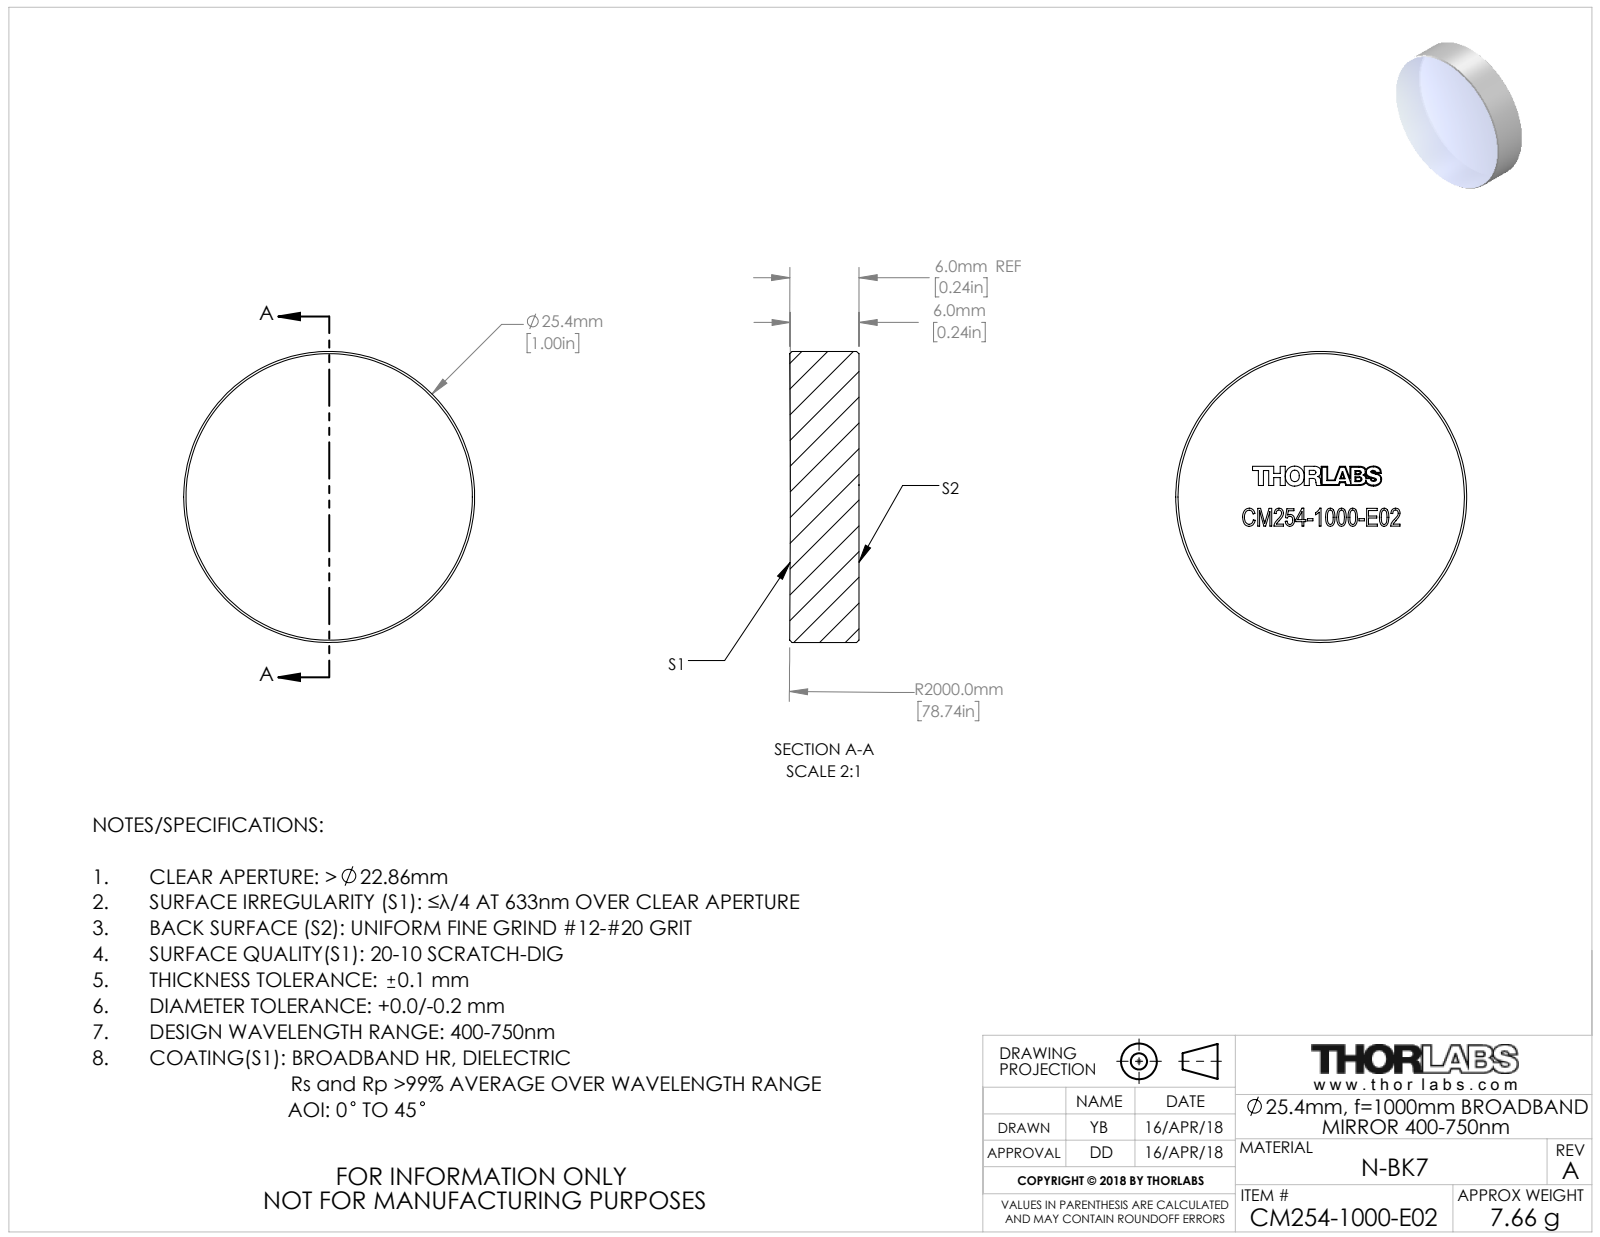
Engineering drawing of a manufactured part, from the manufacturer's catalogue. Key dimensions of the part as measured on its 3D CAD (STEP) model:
Part name (STEP PRODUCT): TTN153318-E0W
STEP written by: SolidWorks 2018 (CONFIG_CONTROL_DESIGN)
Units: millimetres
Bodies: 1 solid, 43 faces (35 planar, 2 cylindrical, 6 other)
Overall size (bounding box): 25.4 × 25.4 × 6.04
Volume: 3 047 mm³ · Surface area: 1 477 mm²
Round bosses / shafts (diameter × count): ⌀25.4 ×1
